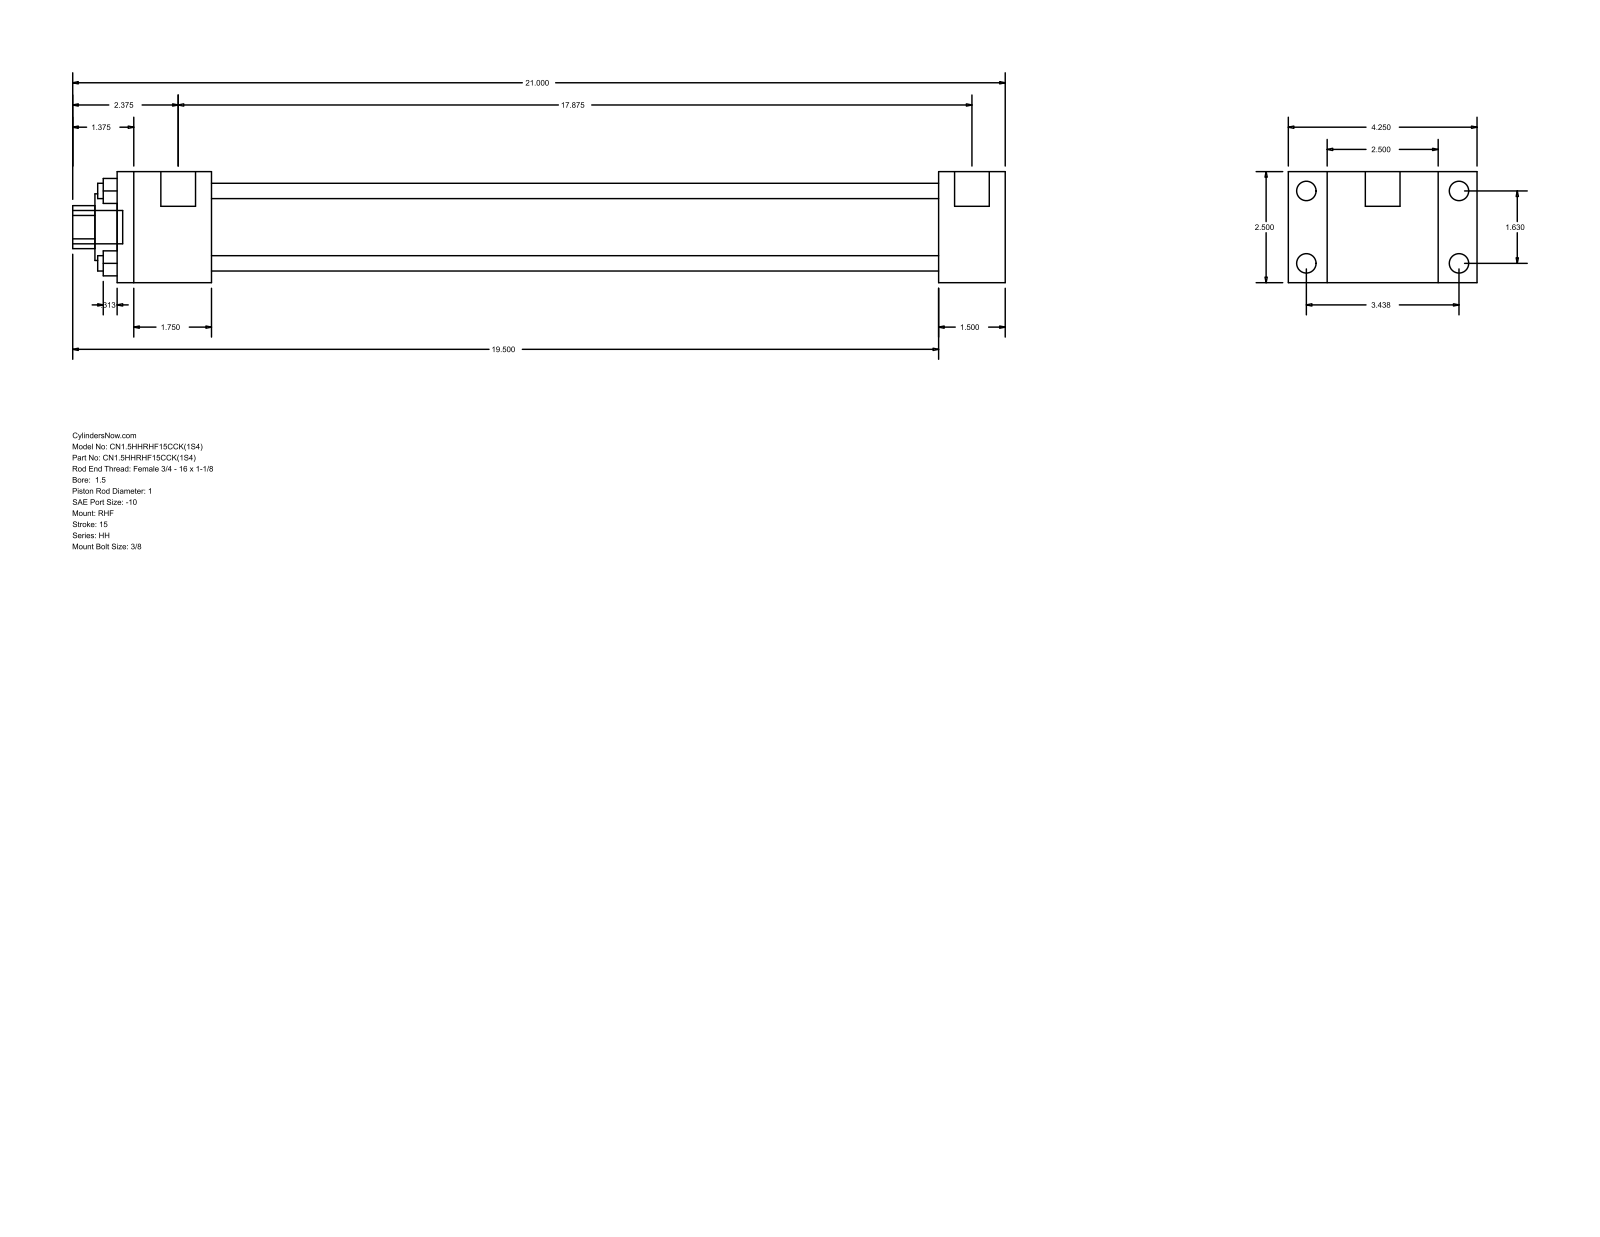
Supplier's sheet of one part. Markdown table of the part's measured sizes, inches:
| quantity | value |
| --- | --- |
| part name | HH_RHF__0150_1 |
| STEP written by | GSSL Pune (CONFIG_CONTROL_DESIGN) |
| units | inches |
| bodies | 0 solids, 88 faces (60 planar, 28 cylindrical, 0 other) |
| overall size | 21 × 4.25 × 2.5 |
| round holes (diameter × count) | 0.345 × 4, 1 × 1, 1.5 × 1, 1.75 × 1 |
| round bosses / shafts (diameter × count) | 0.438 × 4, 0.219 × 4, 0.781 × 2, 0.75 × 1 |
| partial cylindrical surfaces (radius × count) | 0.484 × 1 |
| main face-to-face distances | 2.5, 0.875, 3.375, 1.5, 4.25, 16.375, 17.875, 2.125, 18.5, 20 |
| hole center spacings | 1.152, 1.63, 2.305 |
